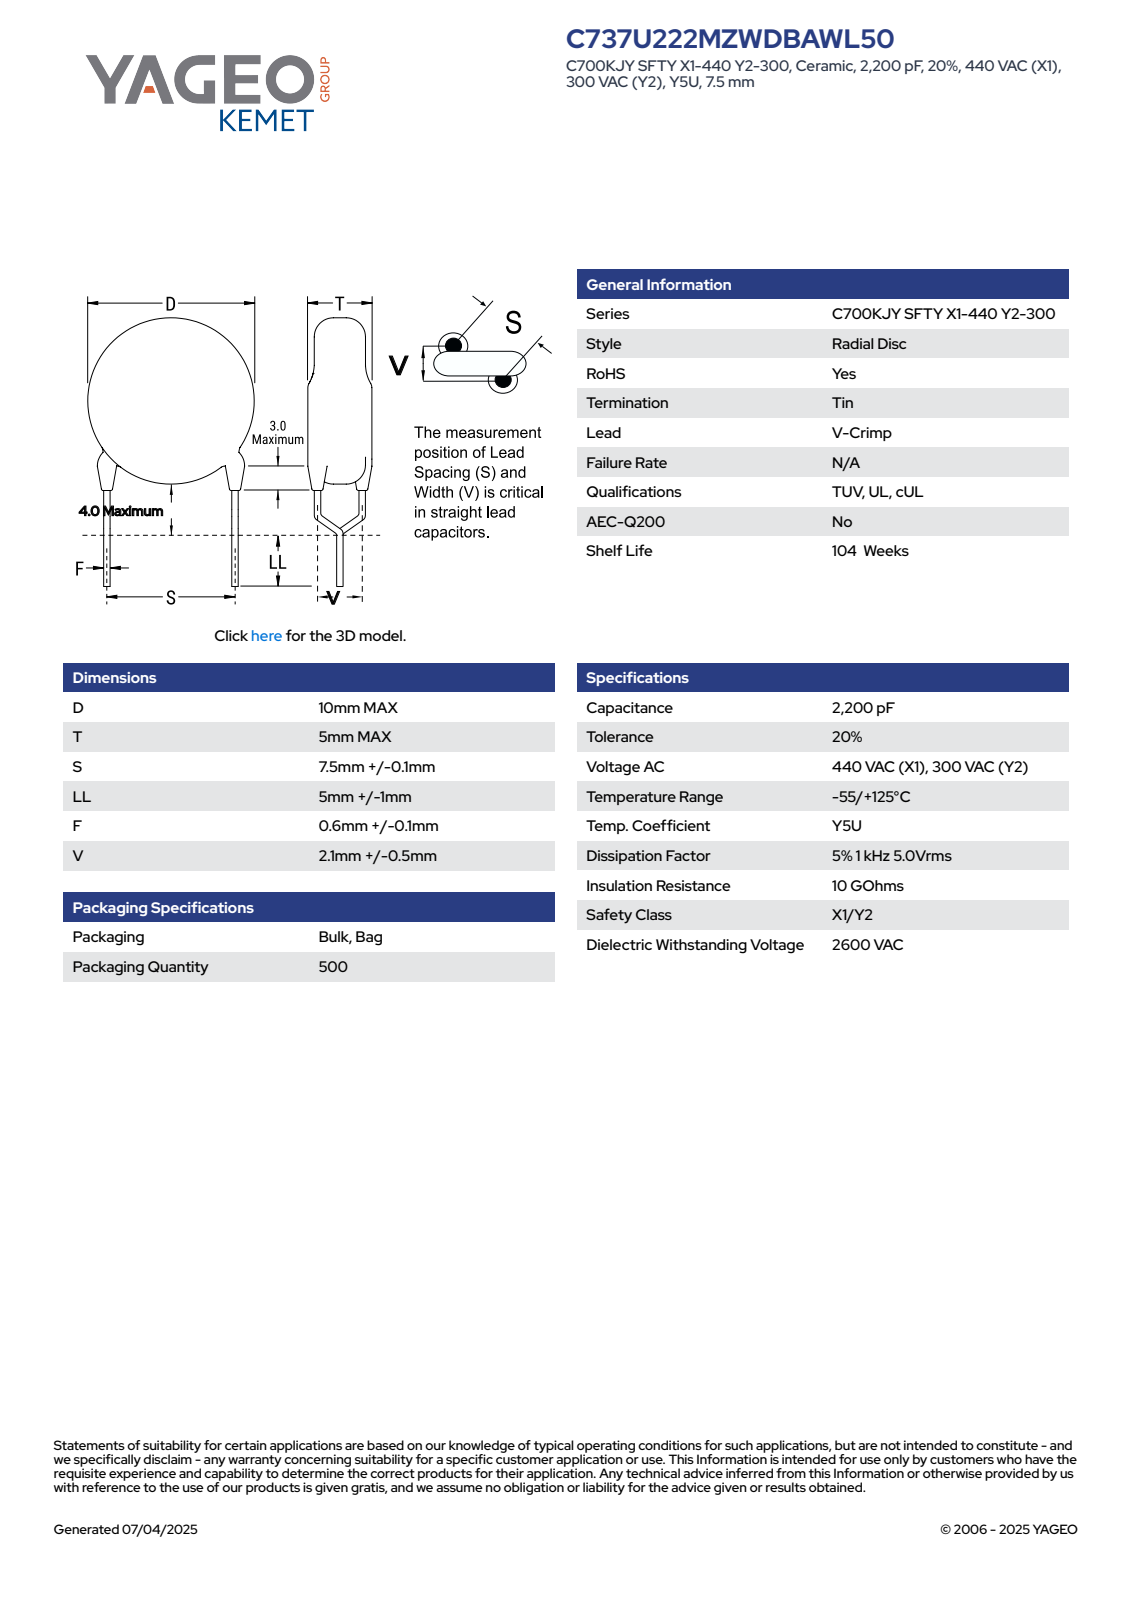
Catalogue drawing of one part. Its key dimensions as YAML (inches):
part_name: "CCD_VC_10X5_D10T5S7.5LL6F0.7V2.1"
step_written_by: "SolidWorks 2021 (AUTOMOTIVE_DESIGN)"
units: inches
bodies: {solids: 4, faces: 88, planar: 63, cylindrical: 21, other: 4}
overall_size: [0.63, 0.394, 0.197]
volume: 0.024
surface_area: 0.516
round_bosses_or_shafts:
  - {diameter: 0.028, count: 6}
  - {diameter: 0.047, count: 2}
  - {diameter: 0.394, count: 1}
partial_cylinders:
  - {radius: 0.024, count: 2}
face_to_face_distances: [0.197, 0.236, 0.038, 0.455, 0.219, 0.417, 0.18, 0.017, 0.043, 0.156]
